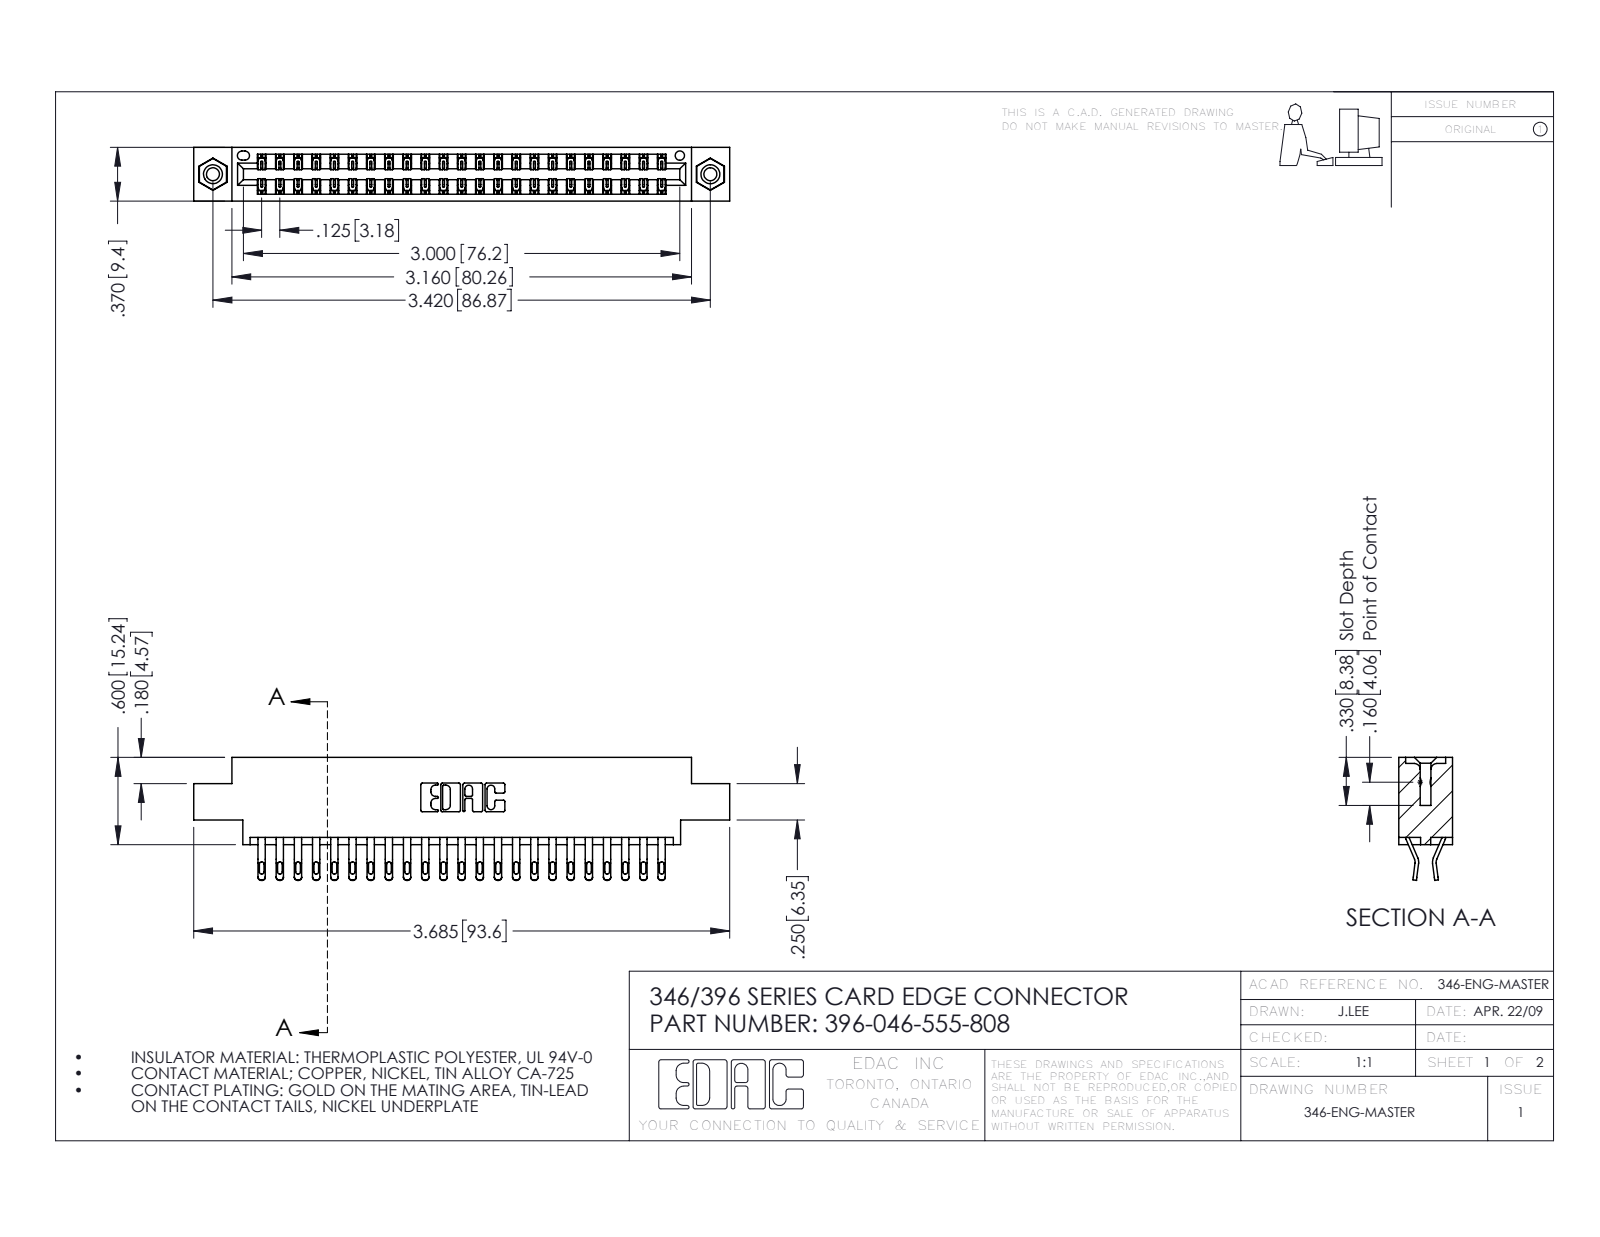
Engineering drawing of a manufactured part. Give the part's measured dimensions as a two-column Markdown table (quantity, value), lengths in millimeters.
| quantity | value |
| --- | --- |
| part name | 345-250-001_345-250-003-102; 396-046-555-808; 346 Part_0.170 Offset - 0.156 Dia-TI; 345-292-001_555 Tail |
| STEP written by | SolidWorks 2016 (CONFIG_CONTROL_DESIGN) |
| units | millimeters |
| bodies | 49 solids, 2854 faces (1630 planar, 1208 cylindrical, 16 other) |
| overall size | 93.6 × 21.5 × 9.4 |
| volume | 8 950 mm³ |
| surface area | 12 680 mm² |
| round holes (diameter × count) | 2.3 × 2, 3.2 × 2, 4 × 2, 1.6 × 1 |
| round bosses / shafts (diameter × count) | 3.9 × 2 |
| partial cylindrical surfaces (radius × count) | 0.4 × 92, 0.5 × 92, 0.2 × 69, 0.3 × 22, 0.2 × 6, 0.8 × 6, 0.7 × 3, 0.3 × 2 |
| main face-to-face distances | 1.2, 8.2, 9.4, 6.4, 0.6, 1.8, 7.6, 7, 5.6, 3.8 |
| hole center spacings | 6.2, 81.6, 86.9 |
